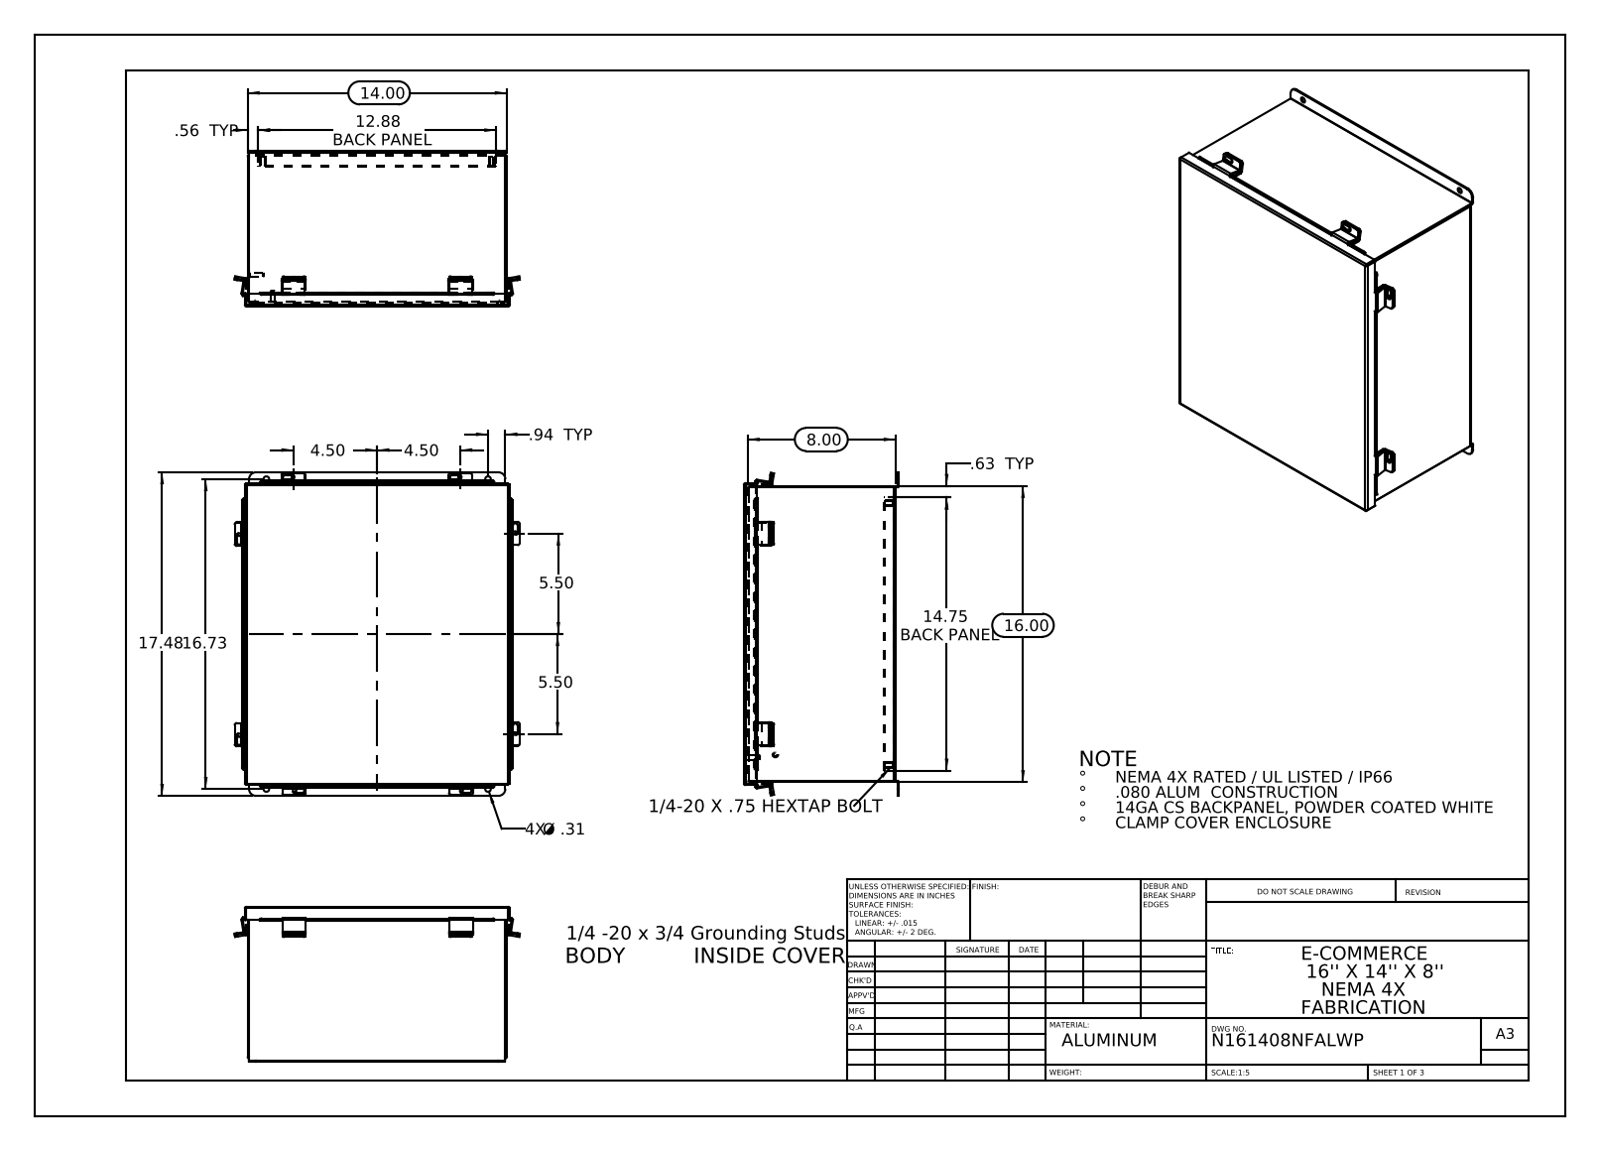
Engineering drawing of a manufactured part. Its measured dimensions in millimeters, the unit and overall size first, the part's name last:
Units: millimetres
Overall size (bounding box): 443.9 × 391.3 × 213.1
Round holes (diameter × count): ⌀6.4 ×12, ⌀4.7 ×4, ⌀7.9 ×4
Round bosses / shafts (diameter × count): ⌀8 ×4, ⌀8 ×2, ⌀6 ×2
Partial cylindrical surfaces — rounded edges, fillets, slot ends (radius × count): R3.2 ×30, R0.2 ×16, R3.4 ×16, R0.3 ×12, R2.2 ×12, R2.1 ×8, R2.5 ×8, R2.1 ×4
Main face-to-face distances: 1.9, 206.5, 353.7, 404.5, 204.5, 208.4, 193.8, 14.6, 12.7, 191.8
Hole centre spacings: 33.4, 311, 391.8, 499.2, 228.6, 275.6, 304.2, 314.3
Volume: 1 510 000 mm³ · Surface area: 1 607 000 mm²
Bodies: 27 solids, 640 faces (420 planar, 200 cylindrical, 20 other)
Part name (STEP PRODUCT): N161408NFSSWP JIC Backpanel; N161408NFSSWP JIC Clamp Bracket; N161408NFSSWP JIC Cover Clamp; N161408NFSSWP (+6 more)
STEP written by: SolidWorks 2013 (CONFIG_CONTROL_DESIGN)
